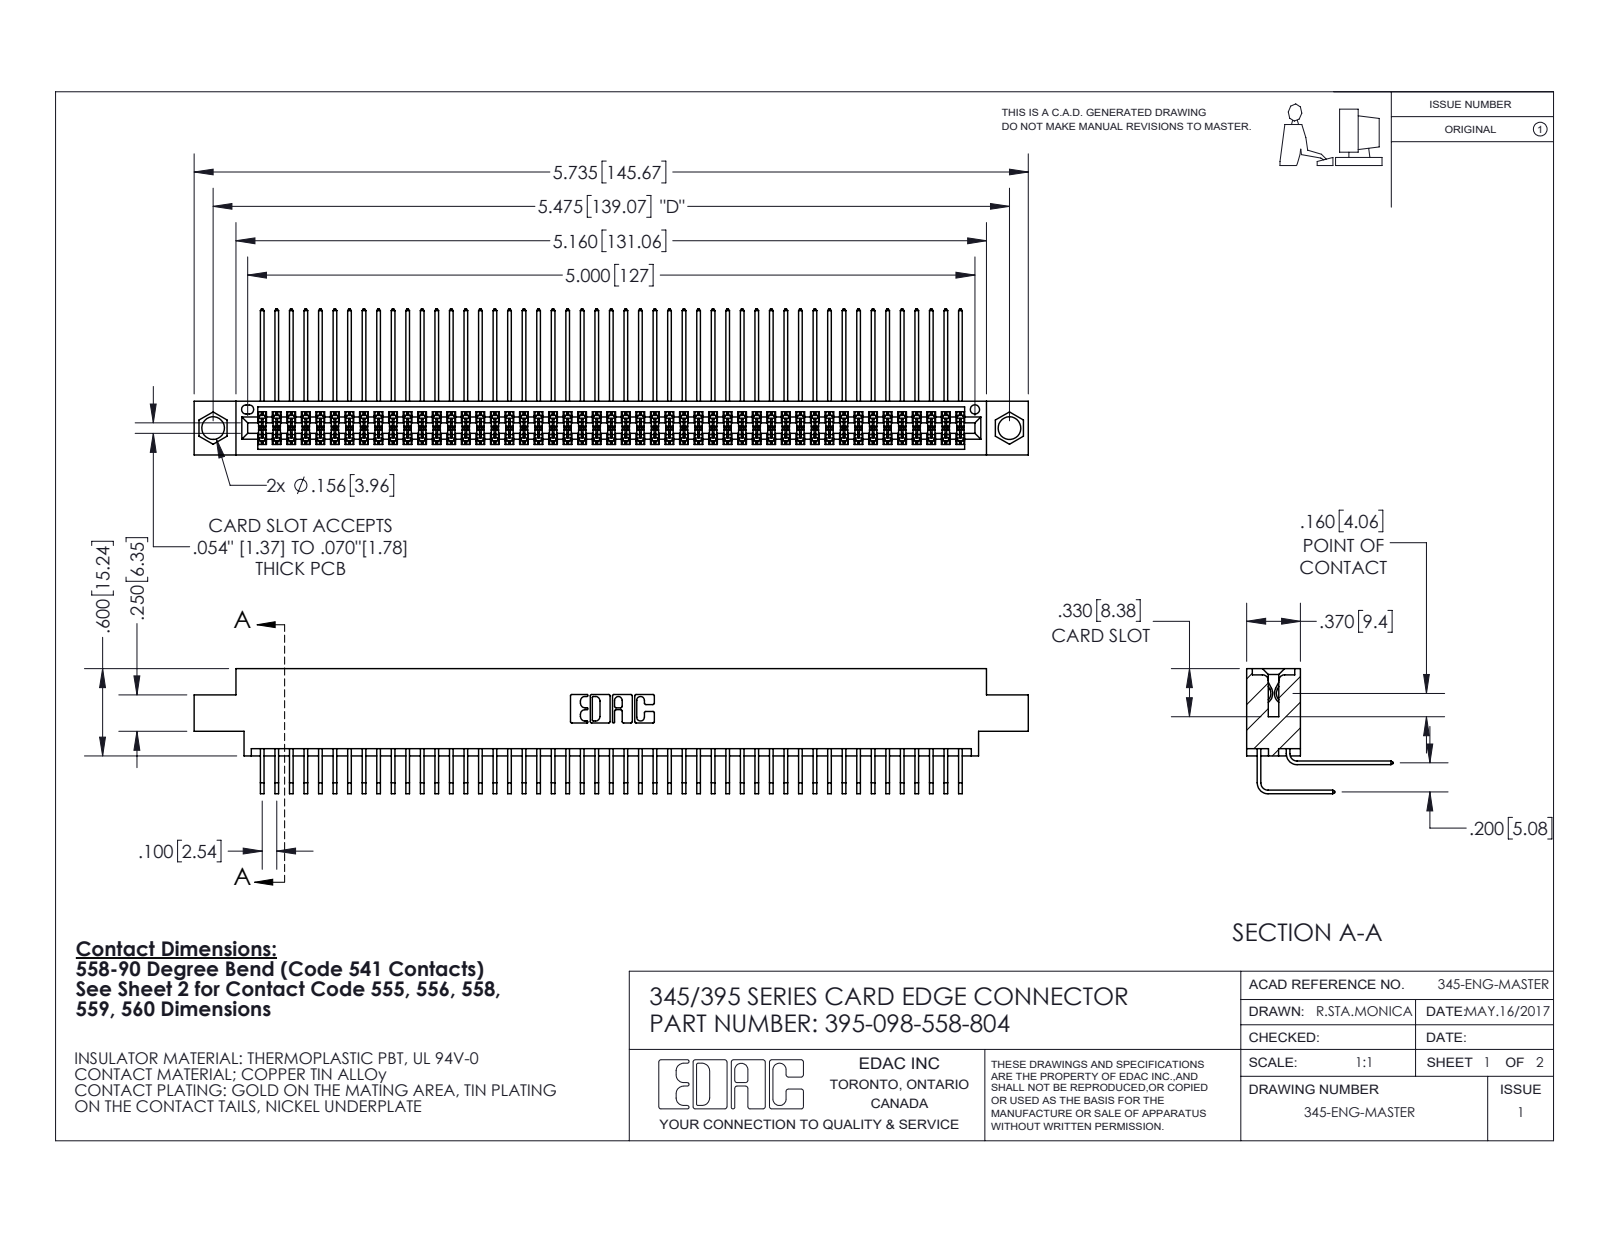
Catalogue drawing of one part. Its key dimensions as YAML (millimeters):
part_name: "345-292-001_558 559 Tail - 1; 345 Part_0.170 Offset - 0.156 Dia-TI; 345-292-001_558 Tail - 2; 395-098-558-804"
step_written_by: "SolidWorks 2020 (CONFIG_CONTROL_DESIGN)"
units: millimeters
bodies: {solids: 99, faces: 5240, planar: 3528, cylindrical: 1712, other: 0}
overall_size: [145.7, 25.5, 21.8]
volume: 14600
surface_area: 24320
round_holes:
  - {diameter: 4, count: 2}
  - {diameter: 1.6, count: 1}
partial_cylinders:
  - {radius: 0.2, count: 196}
  - {radius: 0.3, count: 22}
  - {radius: 0.2, count: 6}
  - {radius: 0.8, count: 6}
  - {radius: 0.7, count: 3}
  - {radius: 0.4, count: 2}
  - {radius: 0.5, count: 2}
  - {radius: 0.6, count: 2}
face_to_face_distances: [1.8, 7.6, 5.1, 9.4, 2.5, 6.9, 0.6, 5.7, 4.4, 0.6]
hole_center_spacings: [6.9, 133.1, 139.1]
